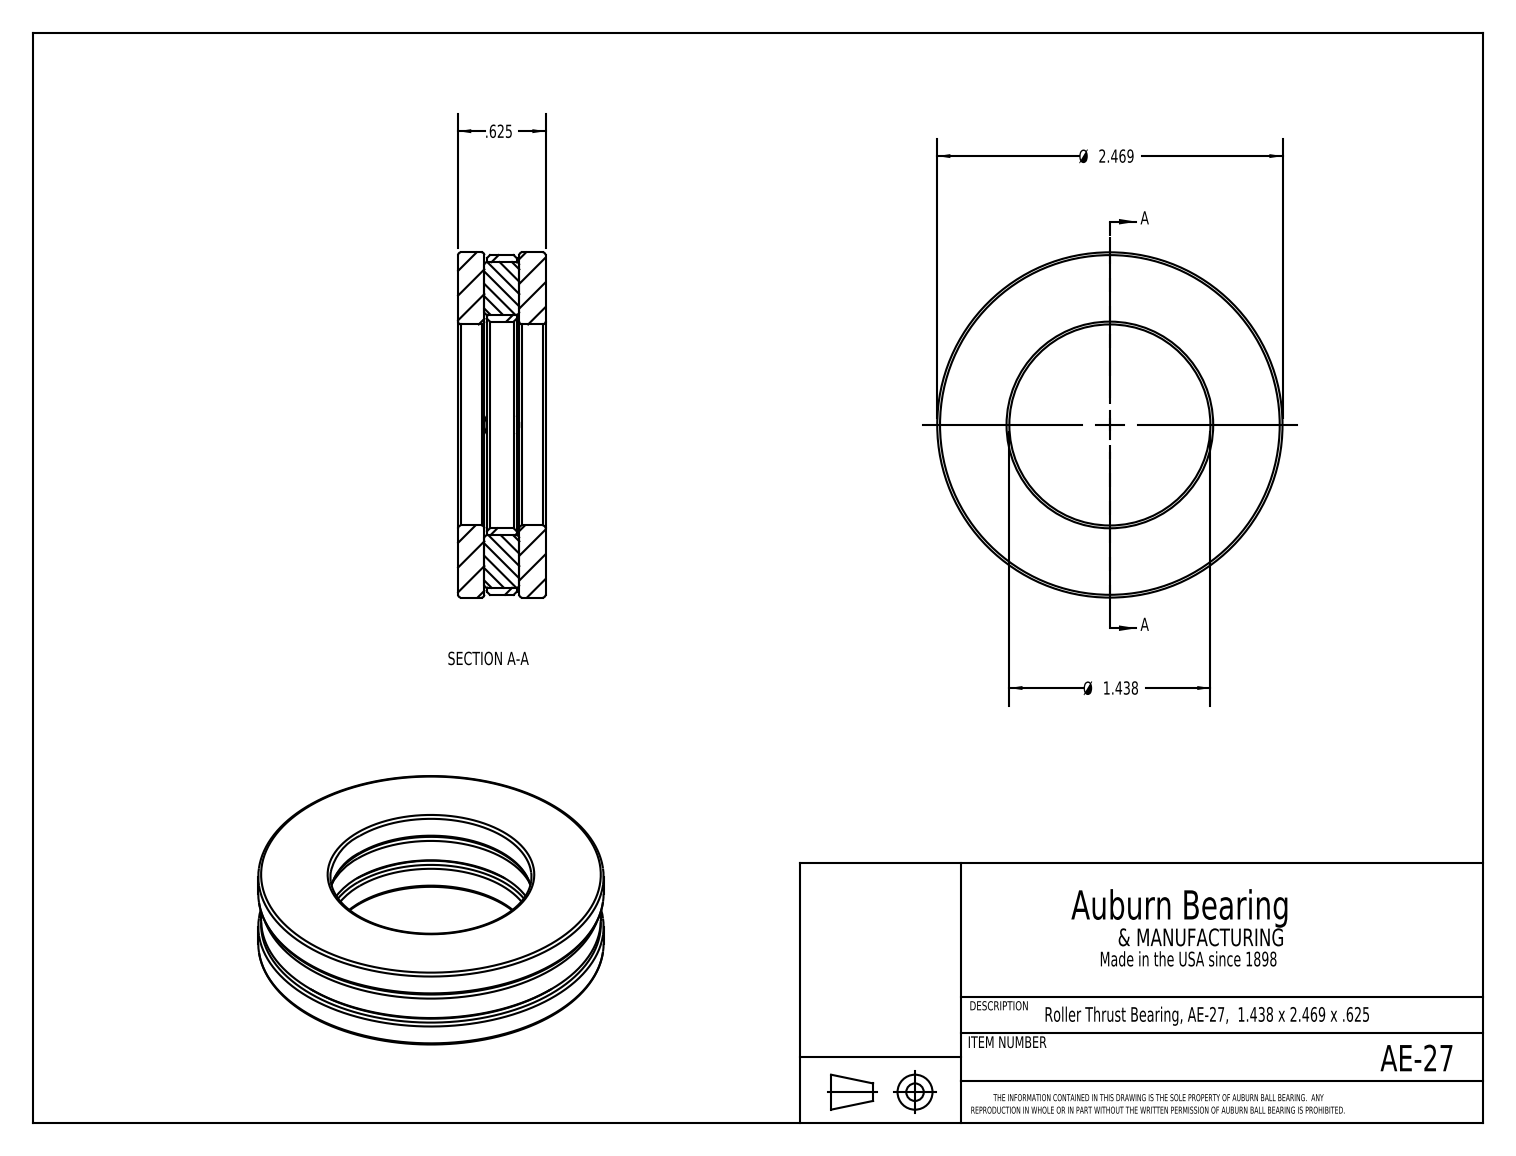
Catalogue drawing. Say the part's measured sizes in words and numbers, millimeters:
The part is named "AE-27". Its 3-D file was written by "SolidWorks 2017 (CONFIG_CONTROL_DESIGN)". It is 7 solids with 60 faces: 30 planar, 10 cylindrical and 20 other. Overall it measures 62.7 by 62.7 by 15.9 millimeters. Its volume is 29 250 cubic millimeters and its surface area 17 280 square millimeters. Round holes: 1 of diameter 36.5, 1 of diameter 37.5. Round bosses or shafts: 2 of diameter 6.4, 1 of diameter 62.7, 1 of diameter 61.7. The main face-to-face distances are 5.3, 10.6, 6.4, 4.7, 11.1, 15.9, 11.1, 4.8, 5.8, 0.5.
